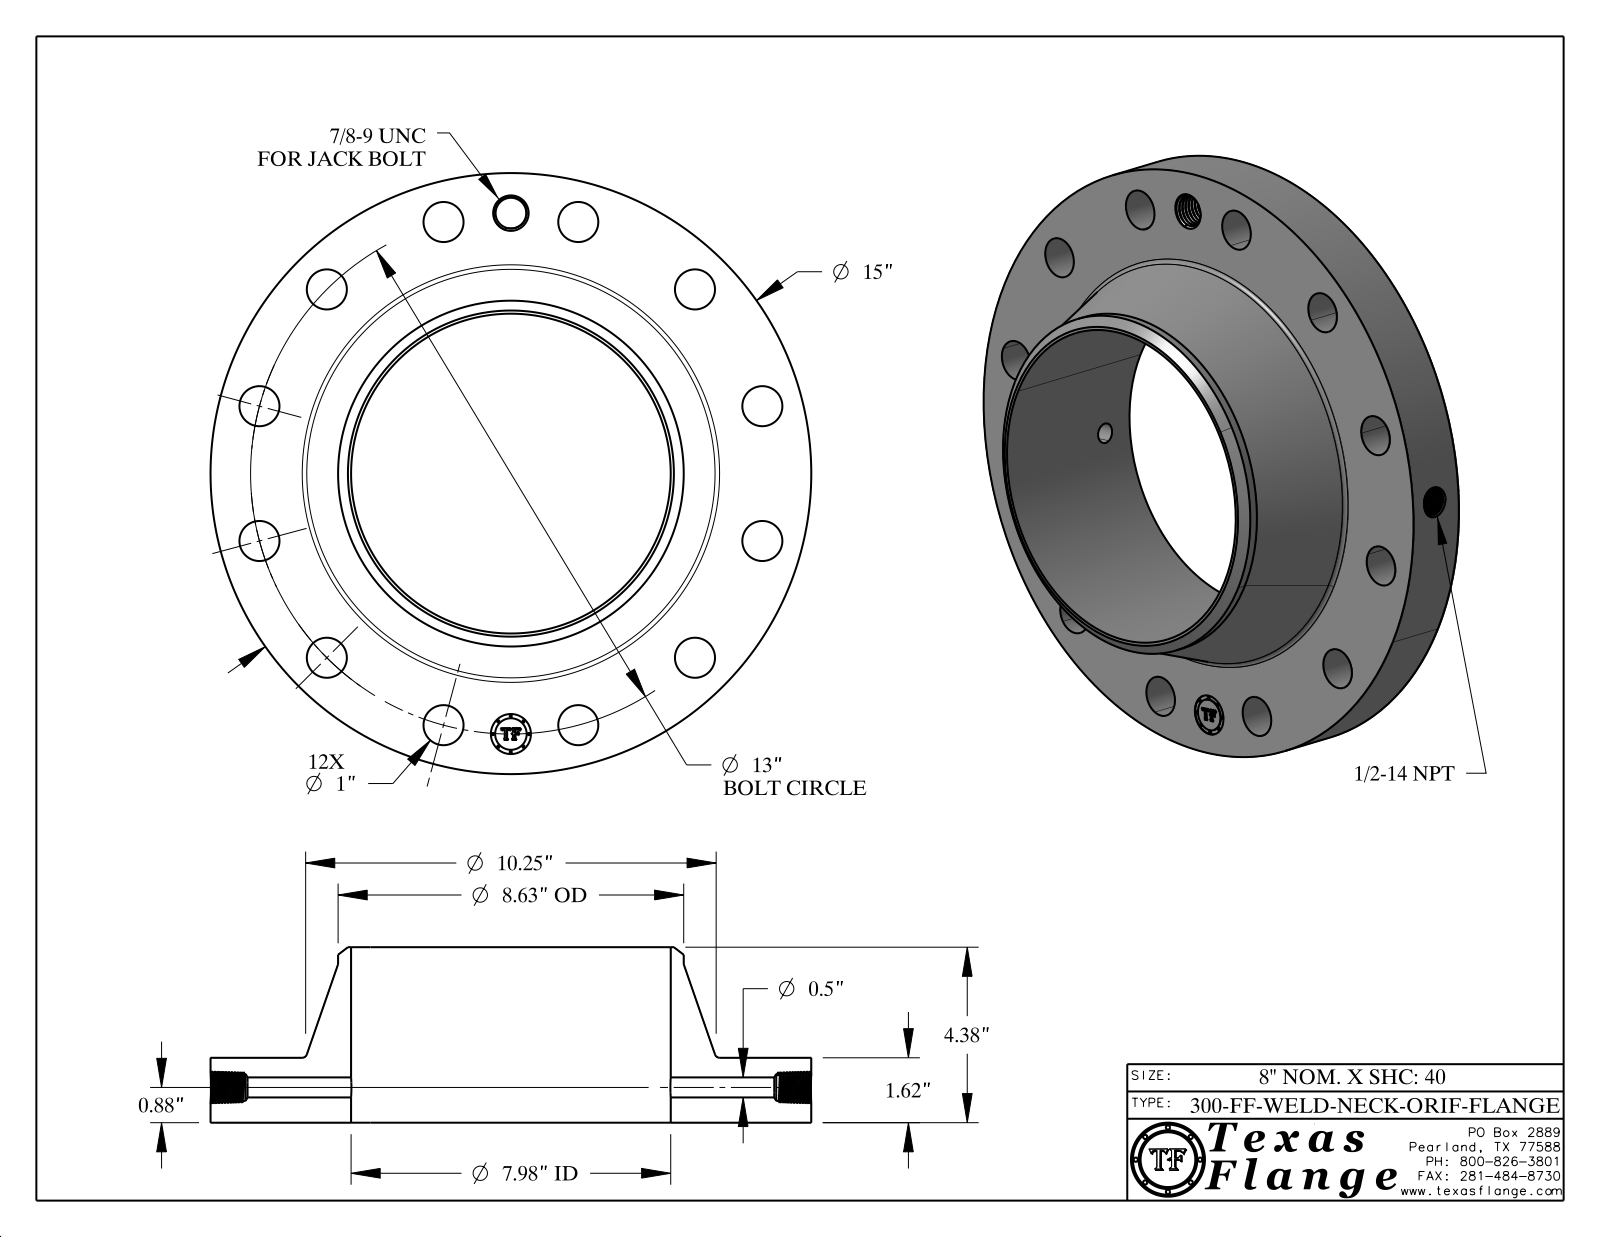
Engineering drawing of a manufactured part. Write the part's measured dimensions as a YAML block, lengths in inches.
part_name: "300-FF-WELD-NECK"
step_written_by: "CATIA V5 STEP AP214 (AUTOMOTIVE_DESIGN)"
units: inches
bodies: {solids: 1, faces: 770, planar: 368, cylindrical: 98, other: 304}
overall_size: [15, 15, 4.38]
volume: 237.4
surface_area: 557.7
round_holes:
  - {diameter: 1, count: 13}
  - {diameter: 0.5, count: 1}
  - {diameter: 0.672, count: 1}
  - {diameter: 0.766, count: 1}
  - {diameter: 7.981, count: 1}
round_bosses_or_shafts:
  - {diameter: 0.061, count: 8}
  - {diameter: 15, count: 1}
  - {diameter: 8.63, count: 1}
  - {diameter: 0.788, count: 1}
face_to_face_distances: [1.62, 4.38, 2.76, 1.605, 0.015, 2.775, 0.298, 0.293, 0.054, 0.248]
hole_center_spacings: [6.5, 3.365, 9.192, 11.258, 12.557, 13, 1.697, 4.975]
